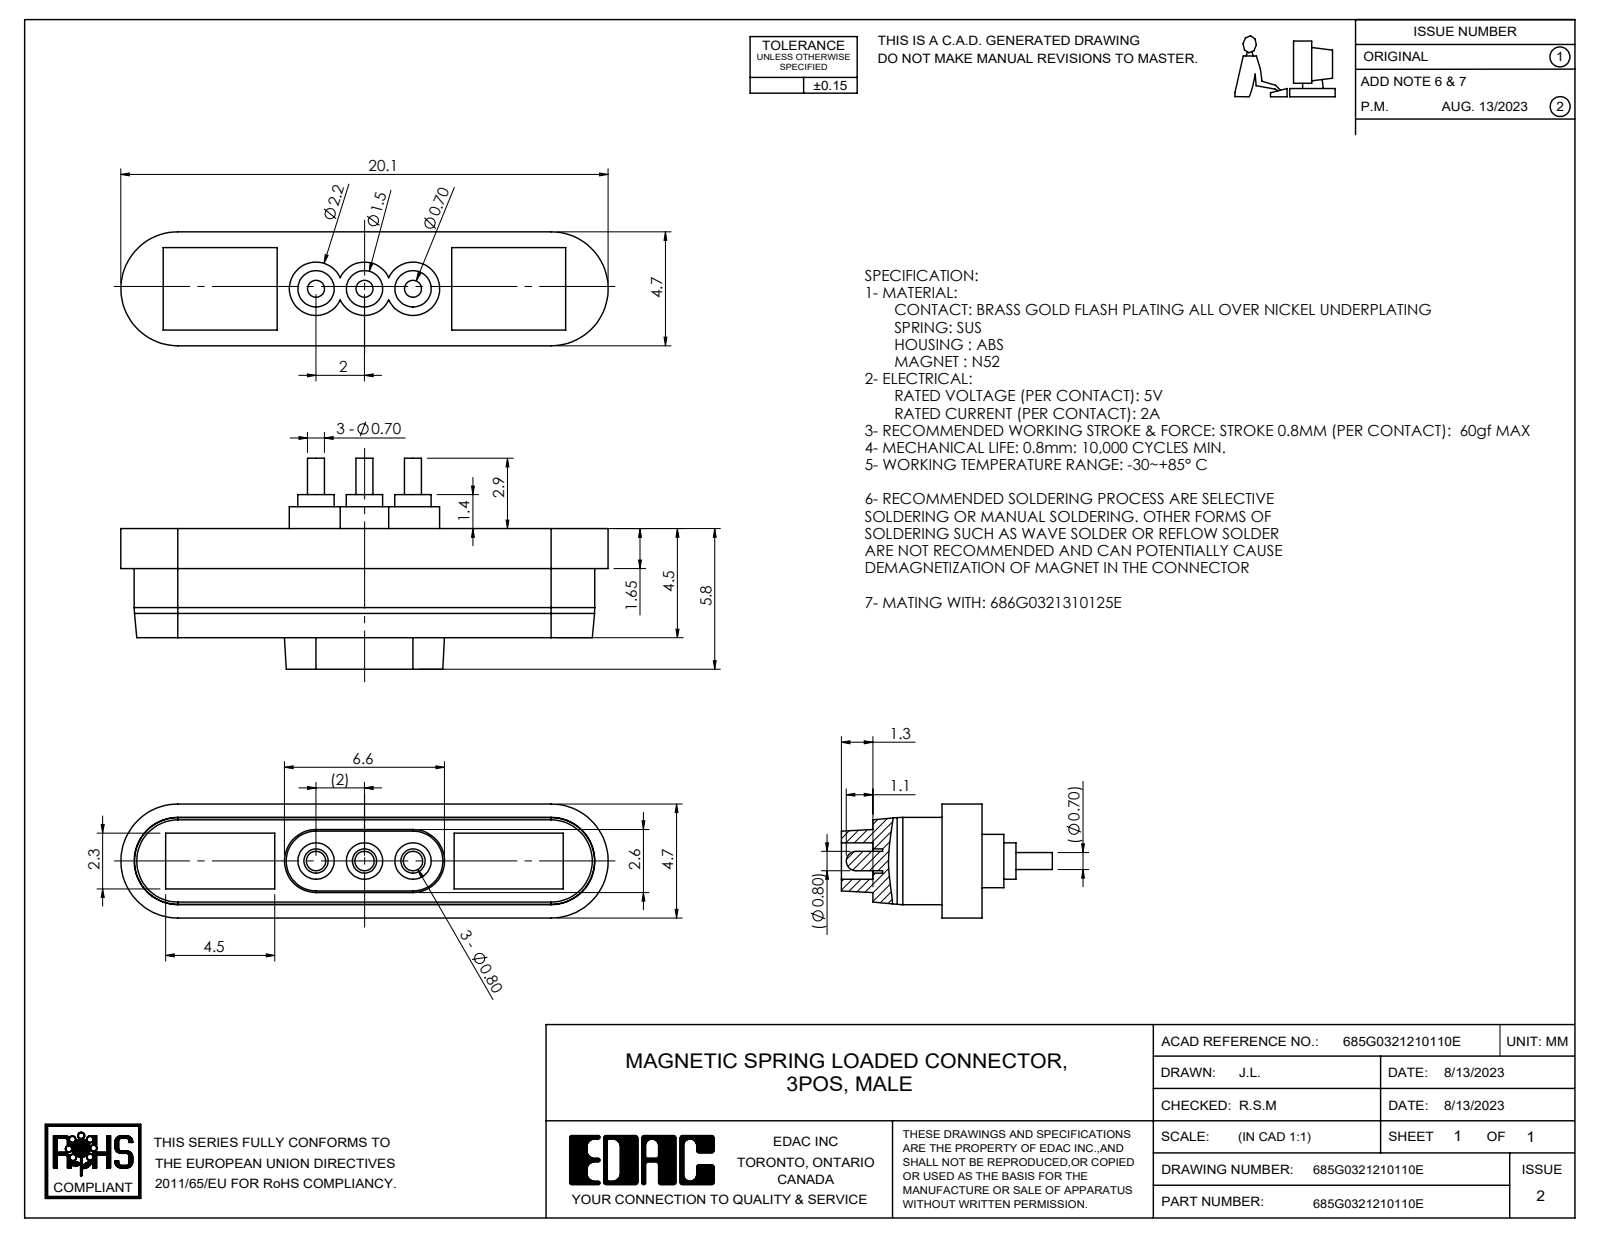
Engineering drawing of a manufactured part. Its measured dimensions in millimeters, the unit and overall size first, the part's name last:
Units: millimetres
Overall size (bounding box): 510.5 × 221 × 119.4
Round holes (diameter × count): ⌀25.4 ×3, ⌀38.1 ×3
Round bosses / shafts (diameter × count): ⌀20.3 ×3, ⌀17.8 ×3, ⌀55.9 ×2
Partial cylindrical surfaces — rounded edges, fillets, slot ends (radius × count): R45.7 ×2, R59.7 ×2, R27.9 ×1
Main face-to-face distances: 14, 105.4, 16.5, 88.9, 72.4, 41.9, 2.5, 119.4, 114.3, 102.9
Hole centre spacings: 50.8, 101.6
Volume: 4 610 000 mm³ · Surface area: 350 100 mm²
Bodies: 1 solid, 102 faces (47 planar, 43 cylindrical, 12 other)
Part name (STEP PRODUCT): 685G0321210110E
STEP written by: SolidWorks 2020 (AUTOMOTIVE_DESIGN)
